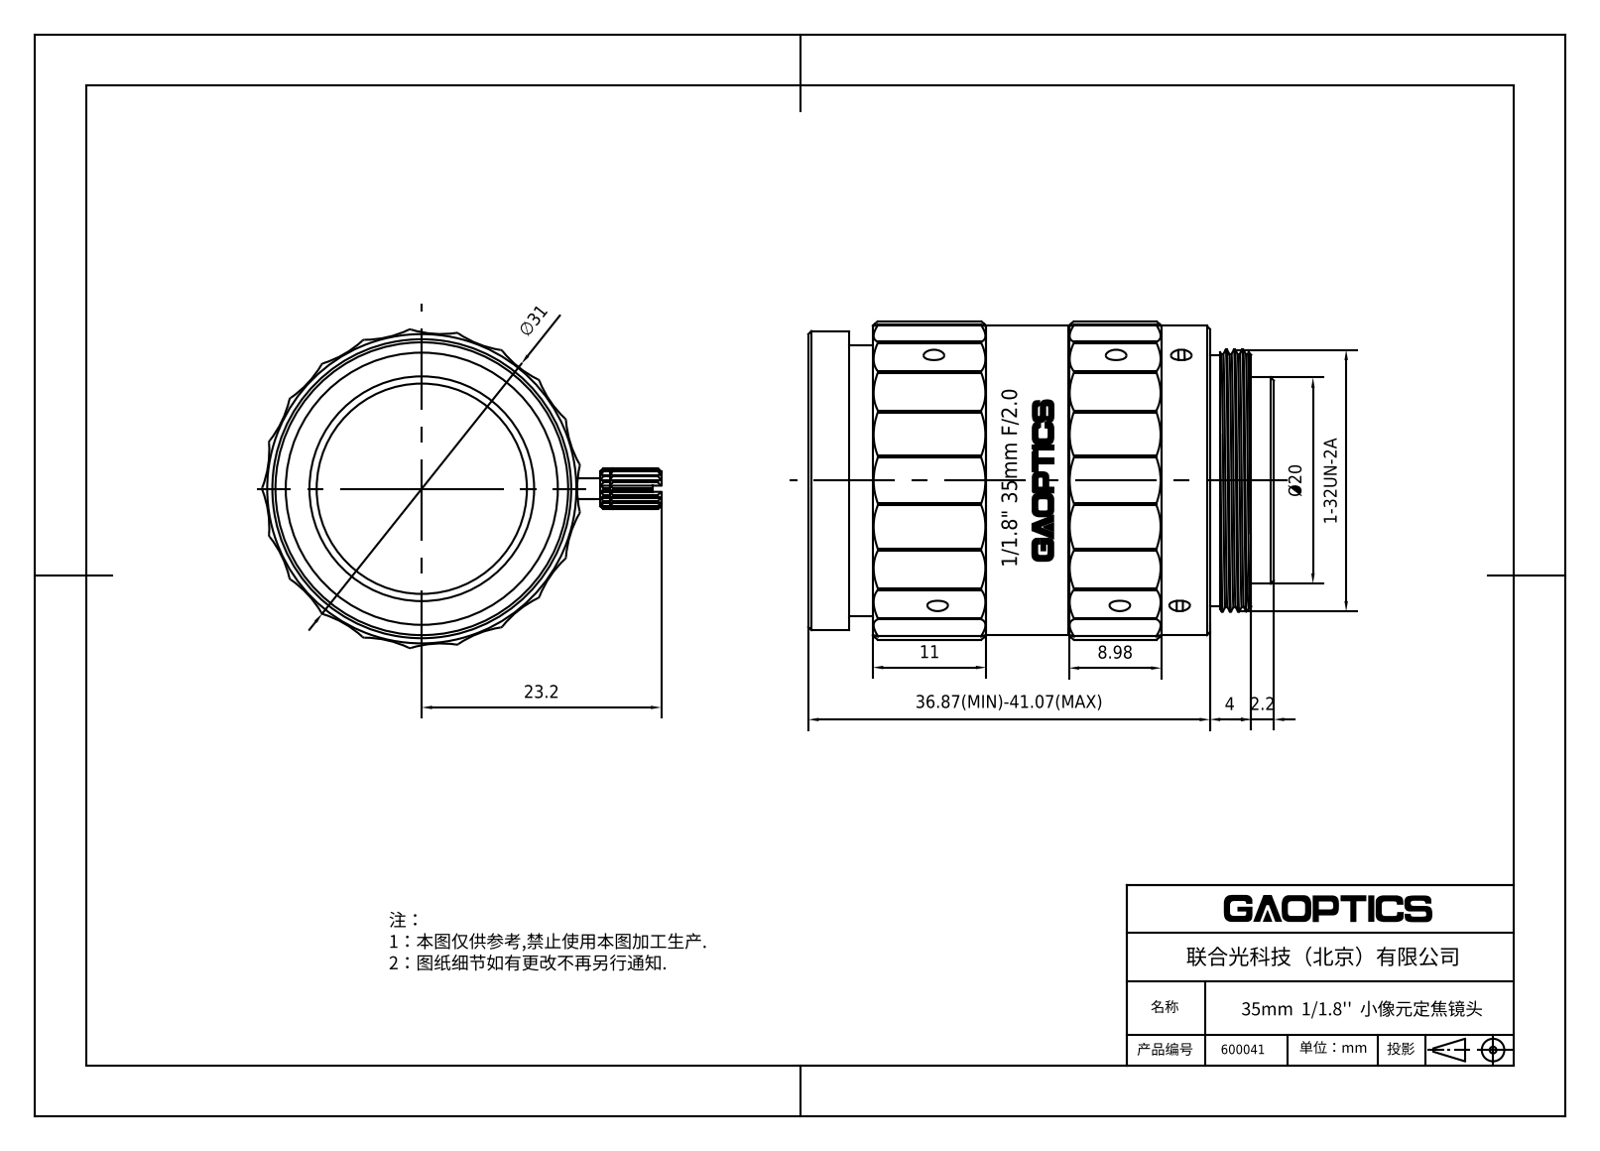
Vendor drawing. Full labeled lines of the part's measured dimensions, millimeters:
Part name (STEP PRODUCT): 600041
STEP written by: SolidWorks 2020 (CONFIG_CONTROL_DESIGN)
Units: millimetres
Bodies: 1 solid, 1690 faces (576 planar, 321 cylindrical, 793 other)
Overall size (bounding box): 44.79 × 38 × 30.91
Volume: 24 567 mm³ · Surface area: 11 268 mm²
Round holes (diameter × count): ⌀1.1 ×3, ⌀2.4 ×3, ⌀2.6 ×3, ⌀1.6 ×2, ⌀13.8 ×1, ⌀15 ×1, ⌀17.6 ×1, ⌀18.2 ×1, ⌀22.5 ×1, ⌀24.3 ×1, ⌀26.2 ×1, ⌀26.4 ×1
Round bosses / shafts (diameter × count): ⌀2.5 ×3, ⌀2 ×2, ⌀30 ×1, ⌀28.9 ×1, ⌀26.3 ×1, ⌀26 ×1, ⌀25.4 ×1, ⌀25.1 ×1
Partial cylindrical surfaces — rounded edges, fillets, slot ends (radius × count): R0.3 ×21, R10 ×21, R1.25 ×6, R0.7 ×3, R1.35 ×3, R2 ×2, R9.85 ×1, R10.05 ×1
Main face-to-face distances: 28, 4.7, 17, 24.89, 4.71, 4.5, 26.38, 26.39, 31.09, 30.89
Hole centre spacings: 3, 17.81, 20.81, 5.99, 11.82, 14.82
